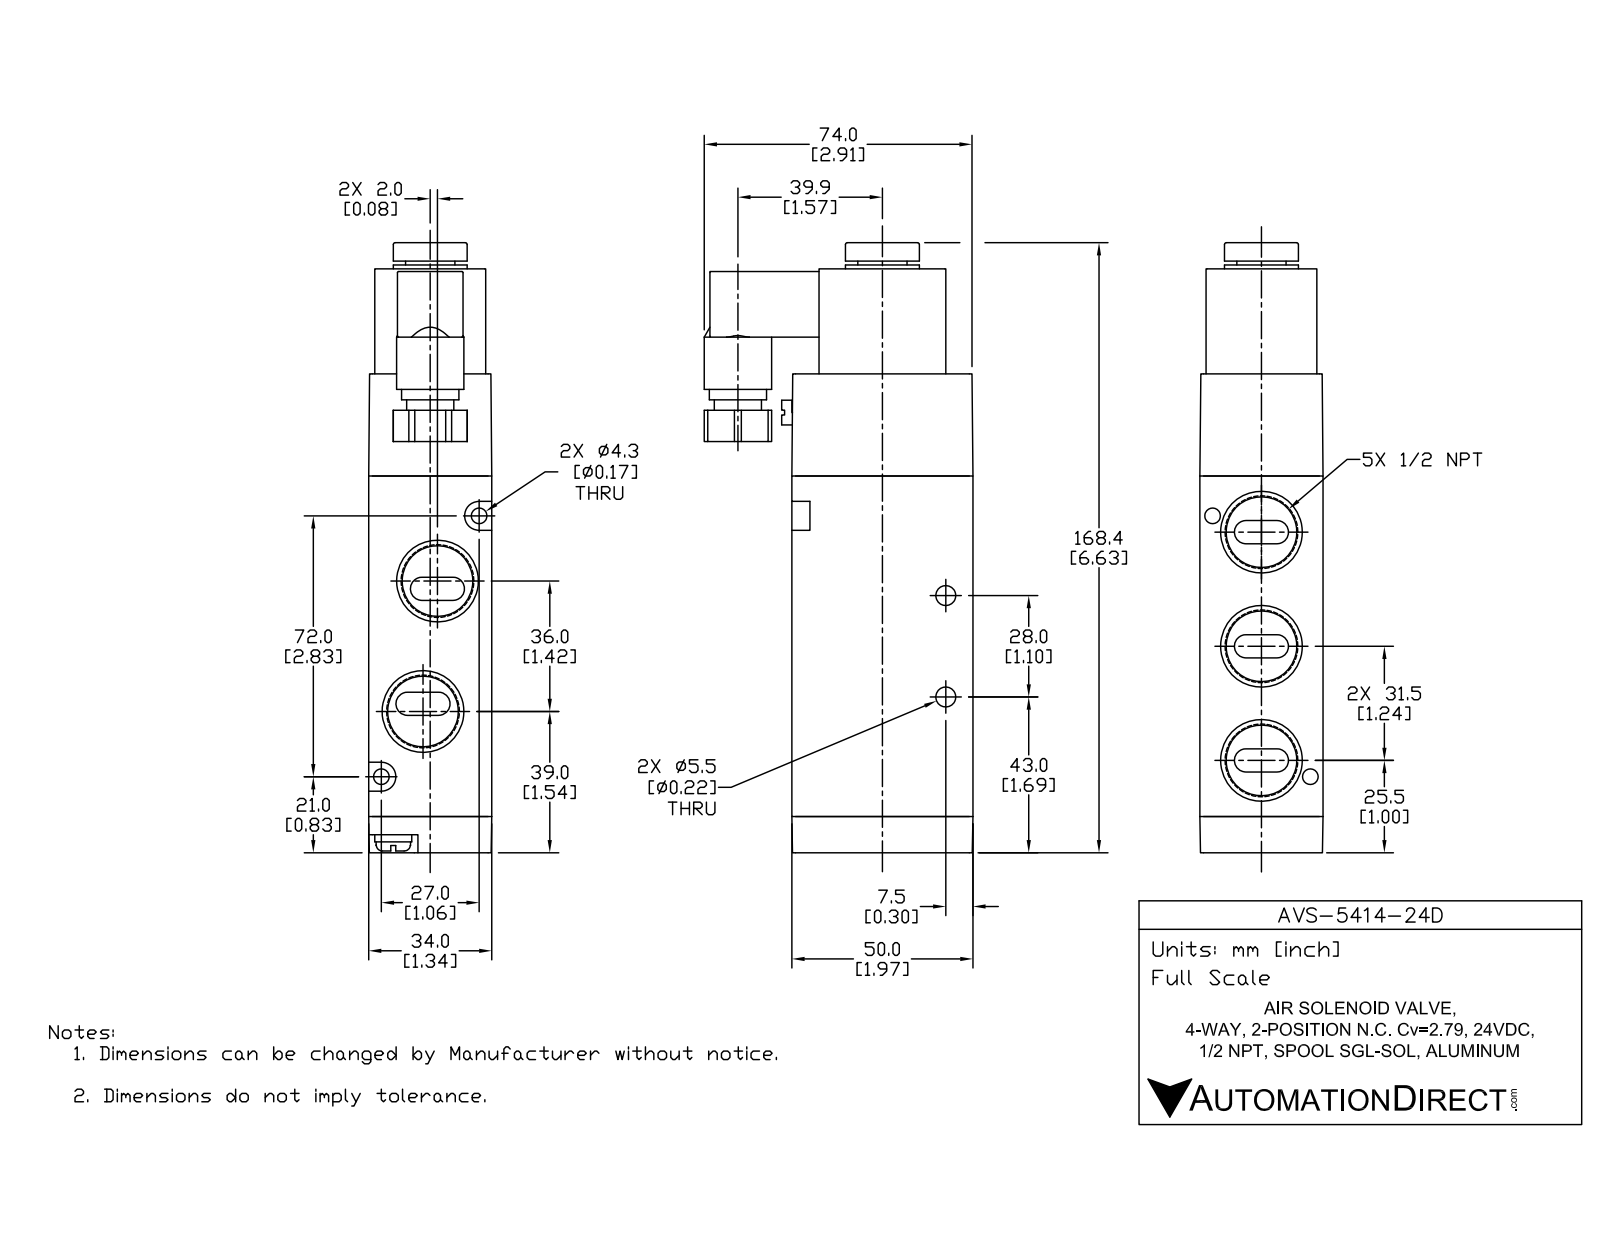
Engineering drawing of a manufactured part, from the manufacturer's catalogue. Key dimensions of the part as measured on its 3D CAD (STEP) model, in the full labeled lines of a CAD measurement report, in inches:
Part name (STEP PRODUCT): AVS-5414-24D
STEP written by: SolidWorks 2015 (CONFIG_CONTROL_DESIGN)
Units: inches
Bodies: 4 solids, 180 faces (80 planar, 73 cylindrical, 27 other)
Overall size (bounding box): 6.634 × 2.921 × 1.339
Volume: 14.83 in³ · Surface area: 75.45 in²
Round holes (diameter × count): ⌀0.703 ×5, ⌀0.217 ×2, ⌀0.169 ×1, ⌀0.173 ×1, ⌀0.366 ×1
Round bosses / shafts (diameter × count): ⌀0.819 ×1, ⌀0.803 ×1, ⌀0.732 ×1, ⌀0.622 ×1, ⌀0.535 ×1, ⌀0.512 ×1, ⌀0.264 ×1
Partial cylindrical surfaces — rounded edges, fillets, slot ends (radius × count): R0.059 ×12, R0.126 ×10, R0.039 ×5, R0.02 ×4, R0.157 ×2
Main face-to-face distances: 1.339, 3.701, 1.969, 0.394, 4.094, 1.11, 1.402, 0.313, 1.026, 0.713
Hole centre spacings: 0.537, 0.56, 0.713, 0.841, 1.24, 1.514, 1.95, 2.212
